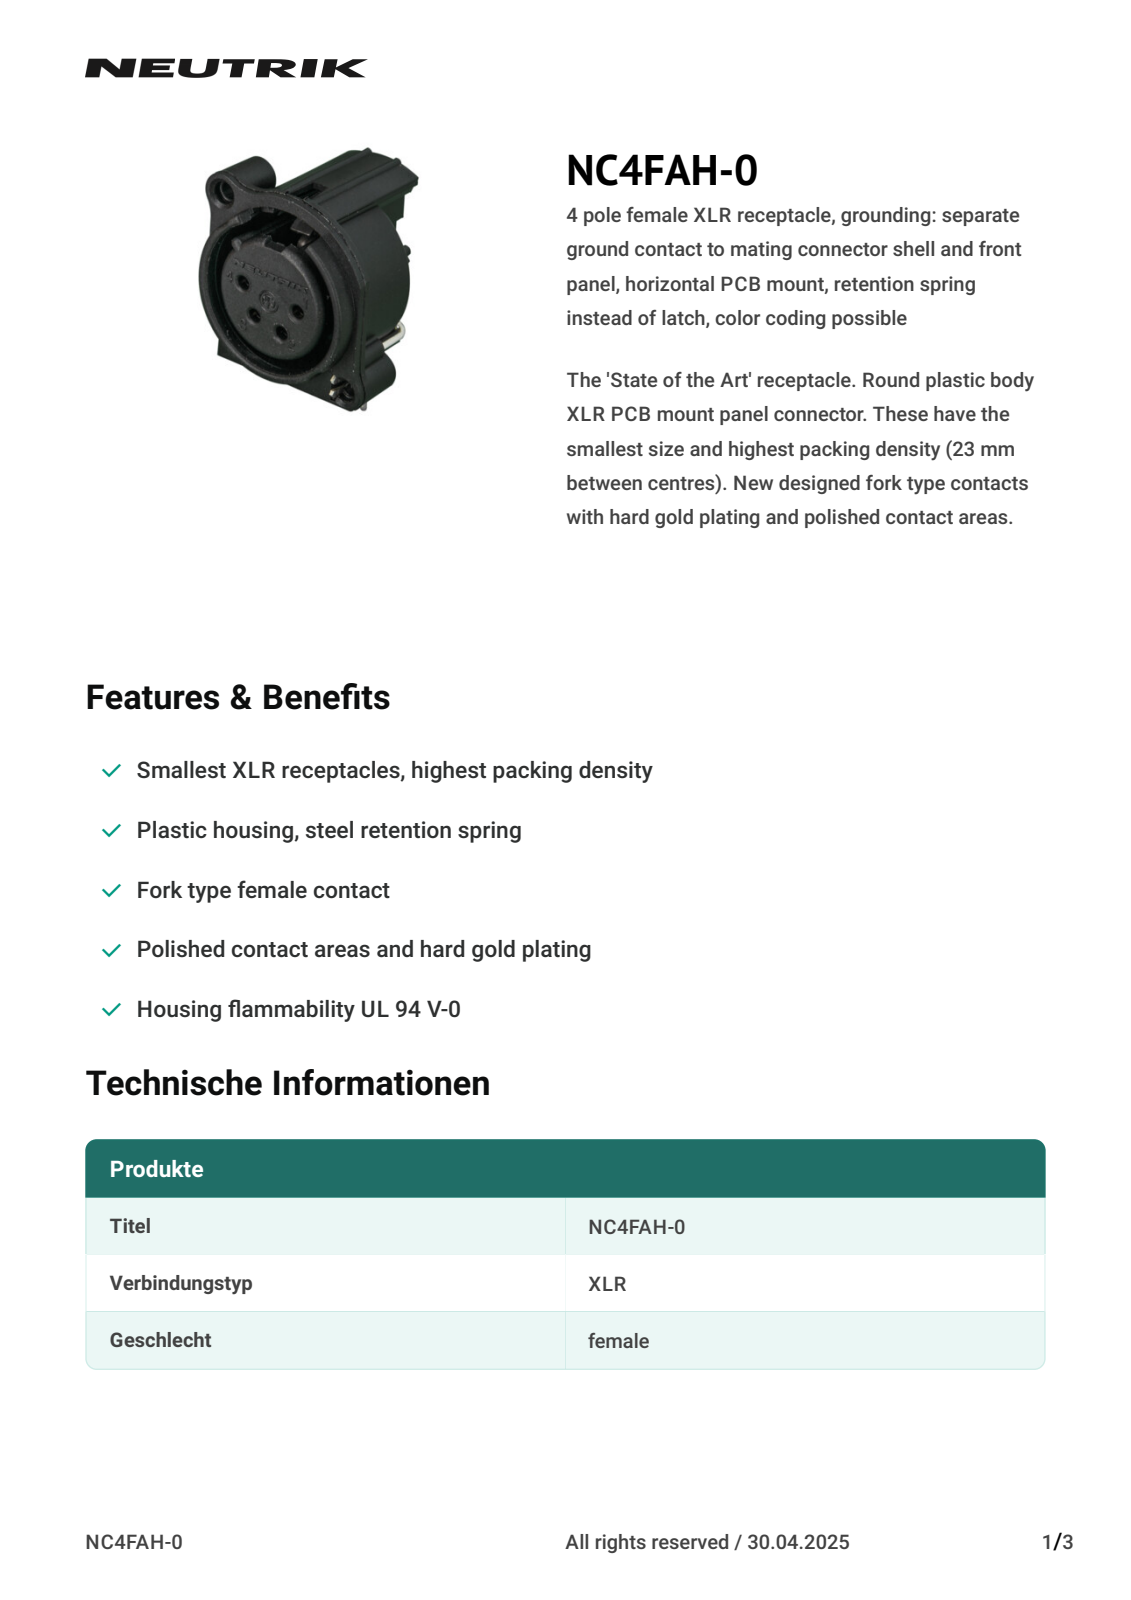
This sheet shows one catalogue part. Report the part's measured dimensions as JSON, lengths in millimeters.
{"part_name": "NC4FAH-0", "step_written_by": "CREO PARAMETRIC BY PTC INC, 2018360 (CONFIG_CONTROL_DESIGN)", "units": "millimeters", "bodies": {"solids": 1, "faces": 1152, "planar": 776, "cylindrical": 269, "other": 107}, "overall_size": [28.51, 25, 22.4], "volume_mm3": 4891, "surface_area_mm2": 6770, "round_holes": [[1.7, 4], [2.35, 2], [1.27, 1], [1.4, 1], [2.5, 1], [3, 1], [19.5, 1], [20.5, 1]], "round_bosses_or_shafts": [[1.5, 2], [22, 1], [15.8, 1], [5.2, 1], [3, 1]], "partial_cylinders_radius": [[0.2, 96], [0.5, 26], [0.12, 9], [1, 6], [0.7, 5], [0.8, 4], [5, 4], [0.75, 3]], "face_to_face_distances": [1, 0.5, 11.8, 2.7, 2, 14.5, 5.6, 0.94, 13, 10.3], "hole_center_spacings": [3.22, 4.27, 11.62, 14, 25.53, 3.55, 4.19, 4.2]}
